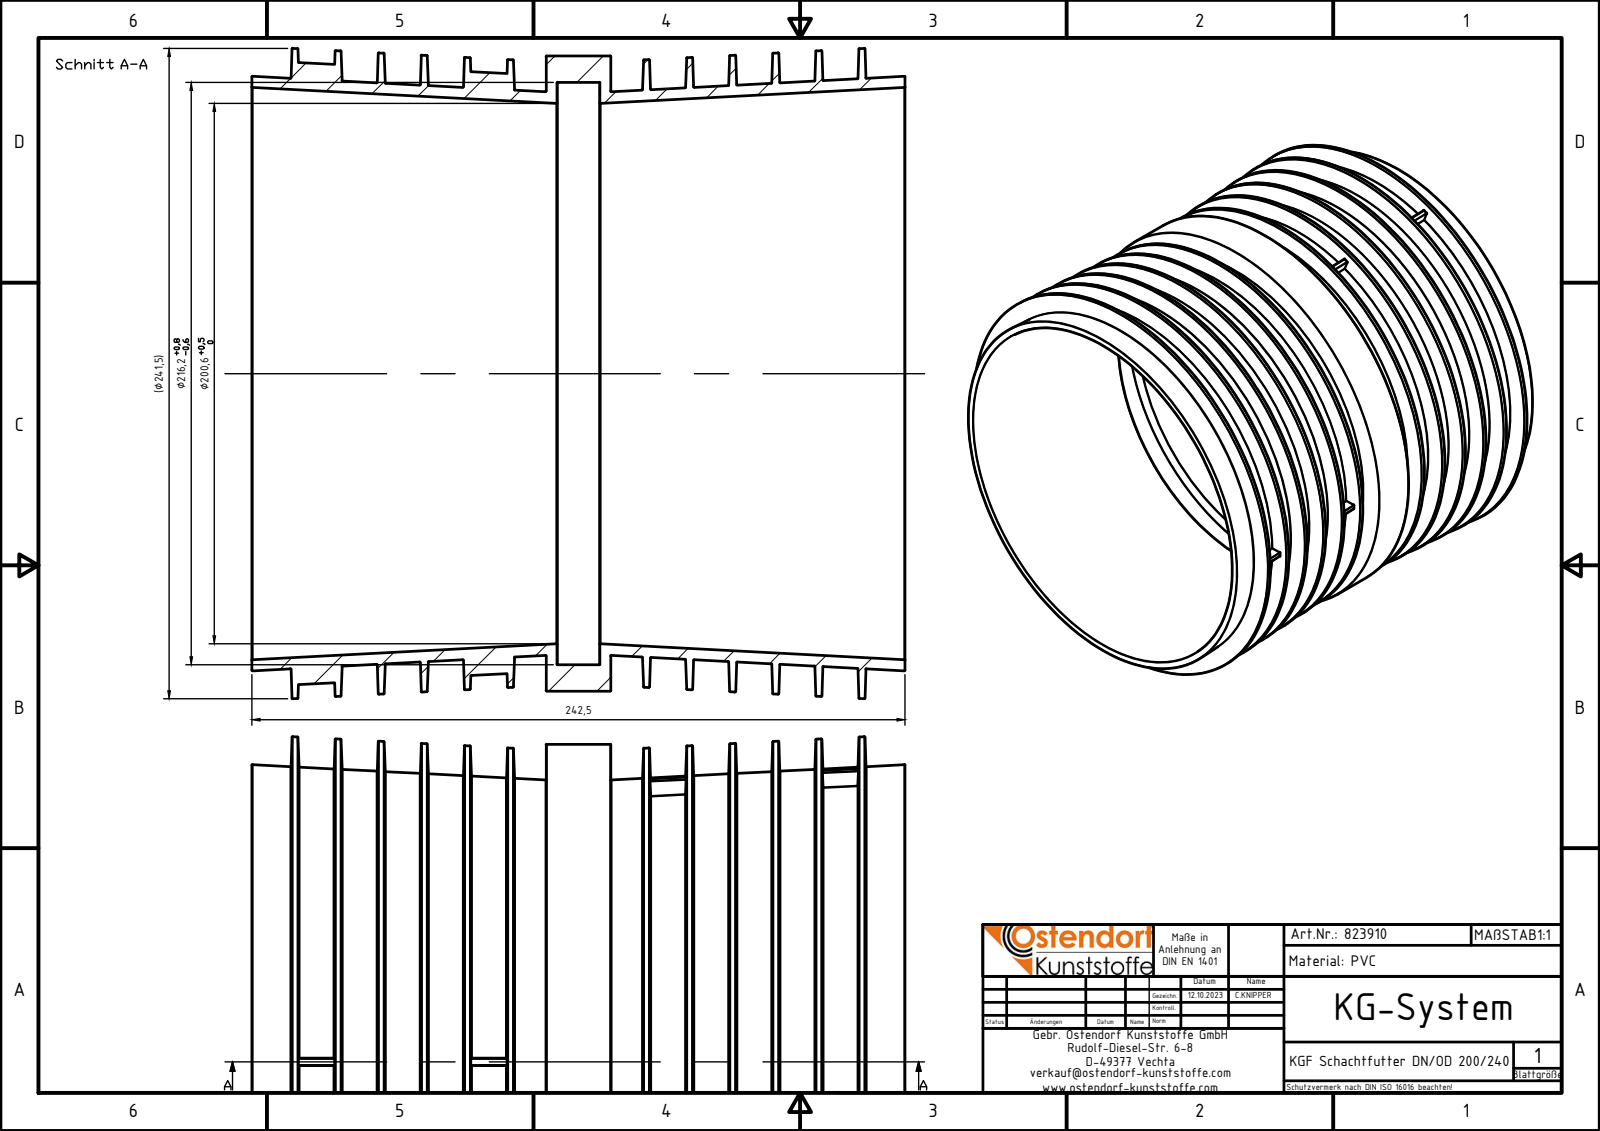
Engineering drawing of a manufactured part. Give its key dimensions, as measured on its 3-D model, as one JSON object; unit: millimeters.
{"part_name": "823910z", "step_written_by": "Autodesk Inventor 2024 (AUTOMOTIVE_DESIGN)", "units": "millimeters", "bodies": {"solids": 1, "faces": 284, "planar": 30, "cylindrical": 18, "other": 236}, "overall_size": [242.5, 241.45, 241.45], "volume_mm3": 1053000, "surface_area_mm2": 541137, "round_holes": [[216.2, 1]], "round_bosses_or_shafts": [[235.8, 1]], "partial_cylinders_radius": [[0.2, 16]], "face_to_face_distances": [4.05, 19.95, 24, 109.25, 113.3, 129.2, 133.25, 15.9, 242.5, 2.7]}
